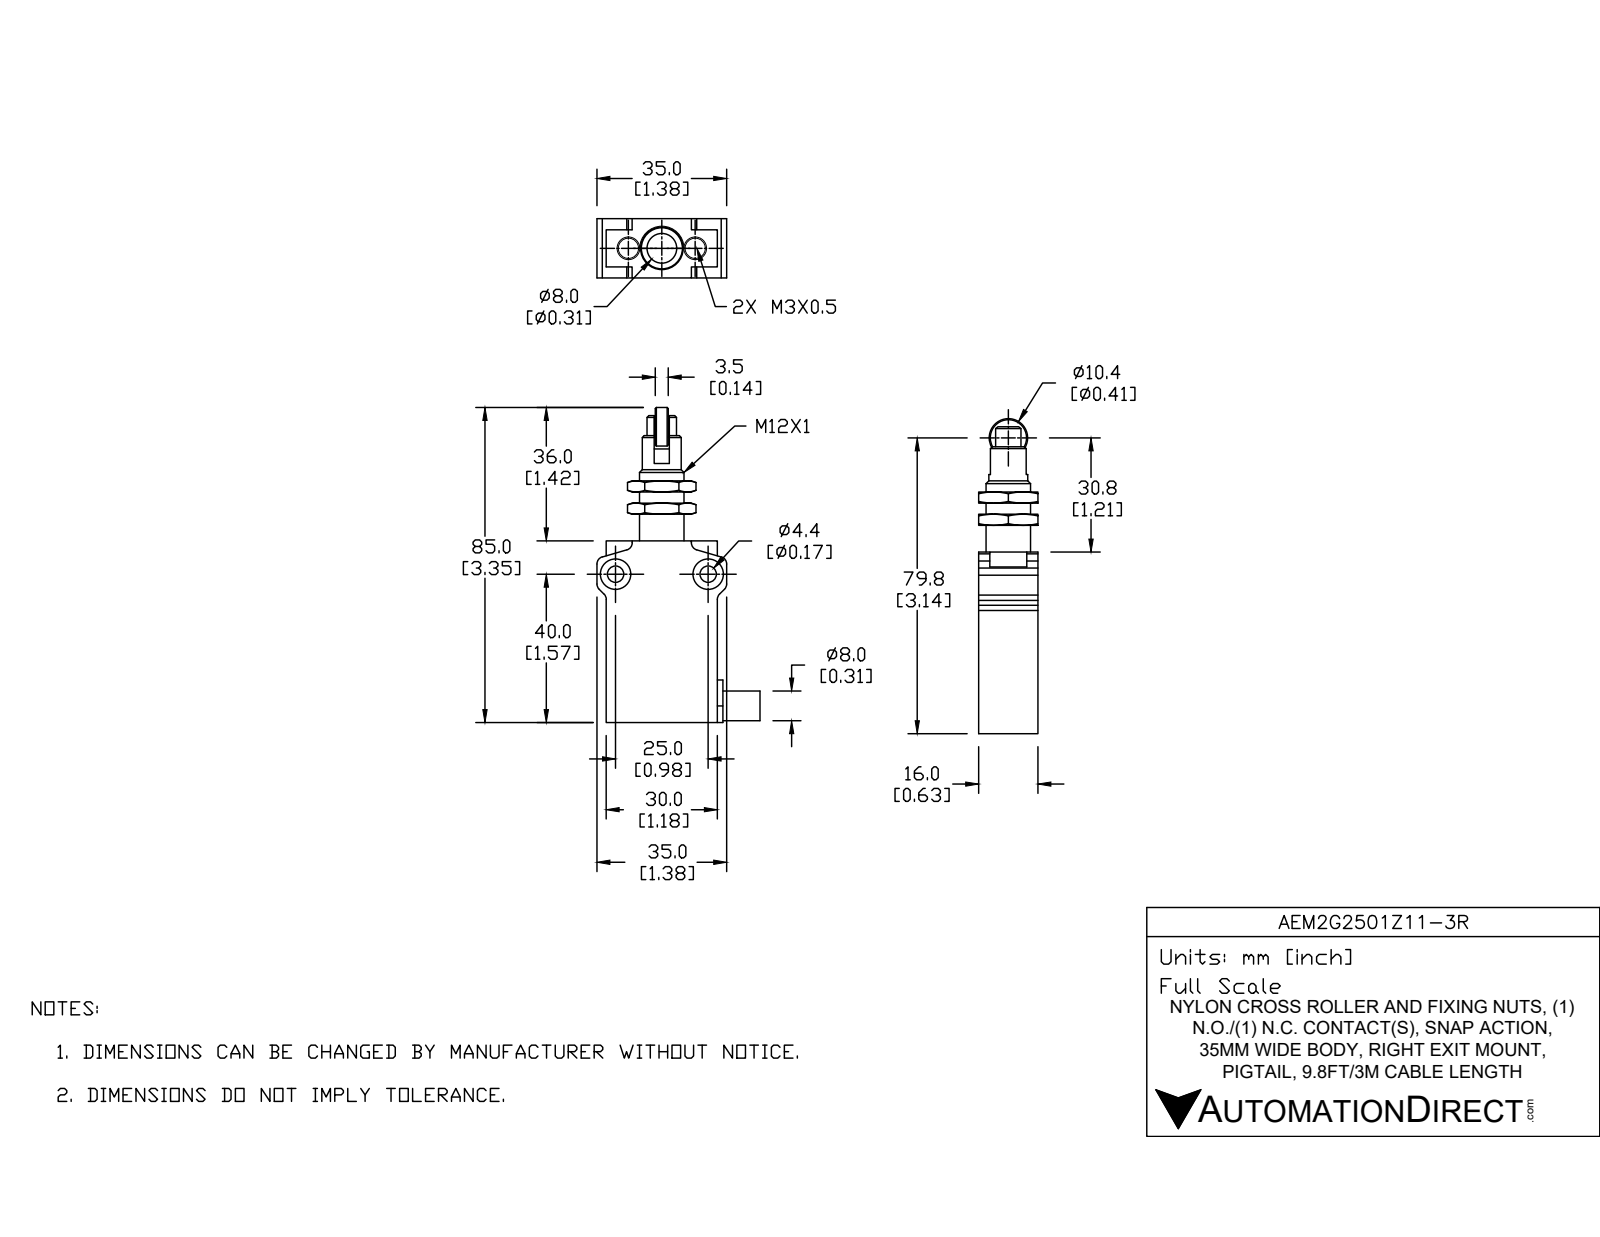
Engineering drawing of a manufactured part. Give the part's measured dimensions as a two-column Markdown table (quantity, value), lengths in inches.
| quantity | value |
| --- | --- |
| part name | AEM2G2501Z11-3R |
| STEP written by | SolidWorks 2017 (AUTOMOTIVE_DESIGN) |
| units | inches |
| bodies | 7 solids, 178 faces (79 planar, 56 cylindrical, 43 other) |
| overall size | 3.346 × 1.87 × 0.727 |
| volume | 1.658 in³ |
| surface area | 17.53 in² |
| round holes (diameter × count) | 0.118 × 2, 0.173 × 2, 0.323 × 2, 0.317 × 1, 0.472 × 1 |
| round bosses / shafts (diameter × count) | 0.413 × 1, 0.409 × 1, 0.323 × 1, 0.313 × 1, 0.22 × 1 |
| partial cylindrical surfaces (radius × count) | 0.079 × 8, 0.256 × 1 |
| main face-to-face distances | 0.63, 1.181, 0.472, 0.118, 0.236, 1.929, 1.74, 0.189, 0.354, 0.157 |
| hole center spacings | 0.374, 0.748, 0.984 |
